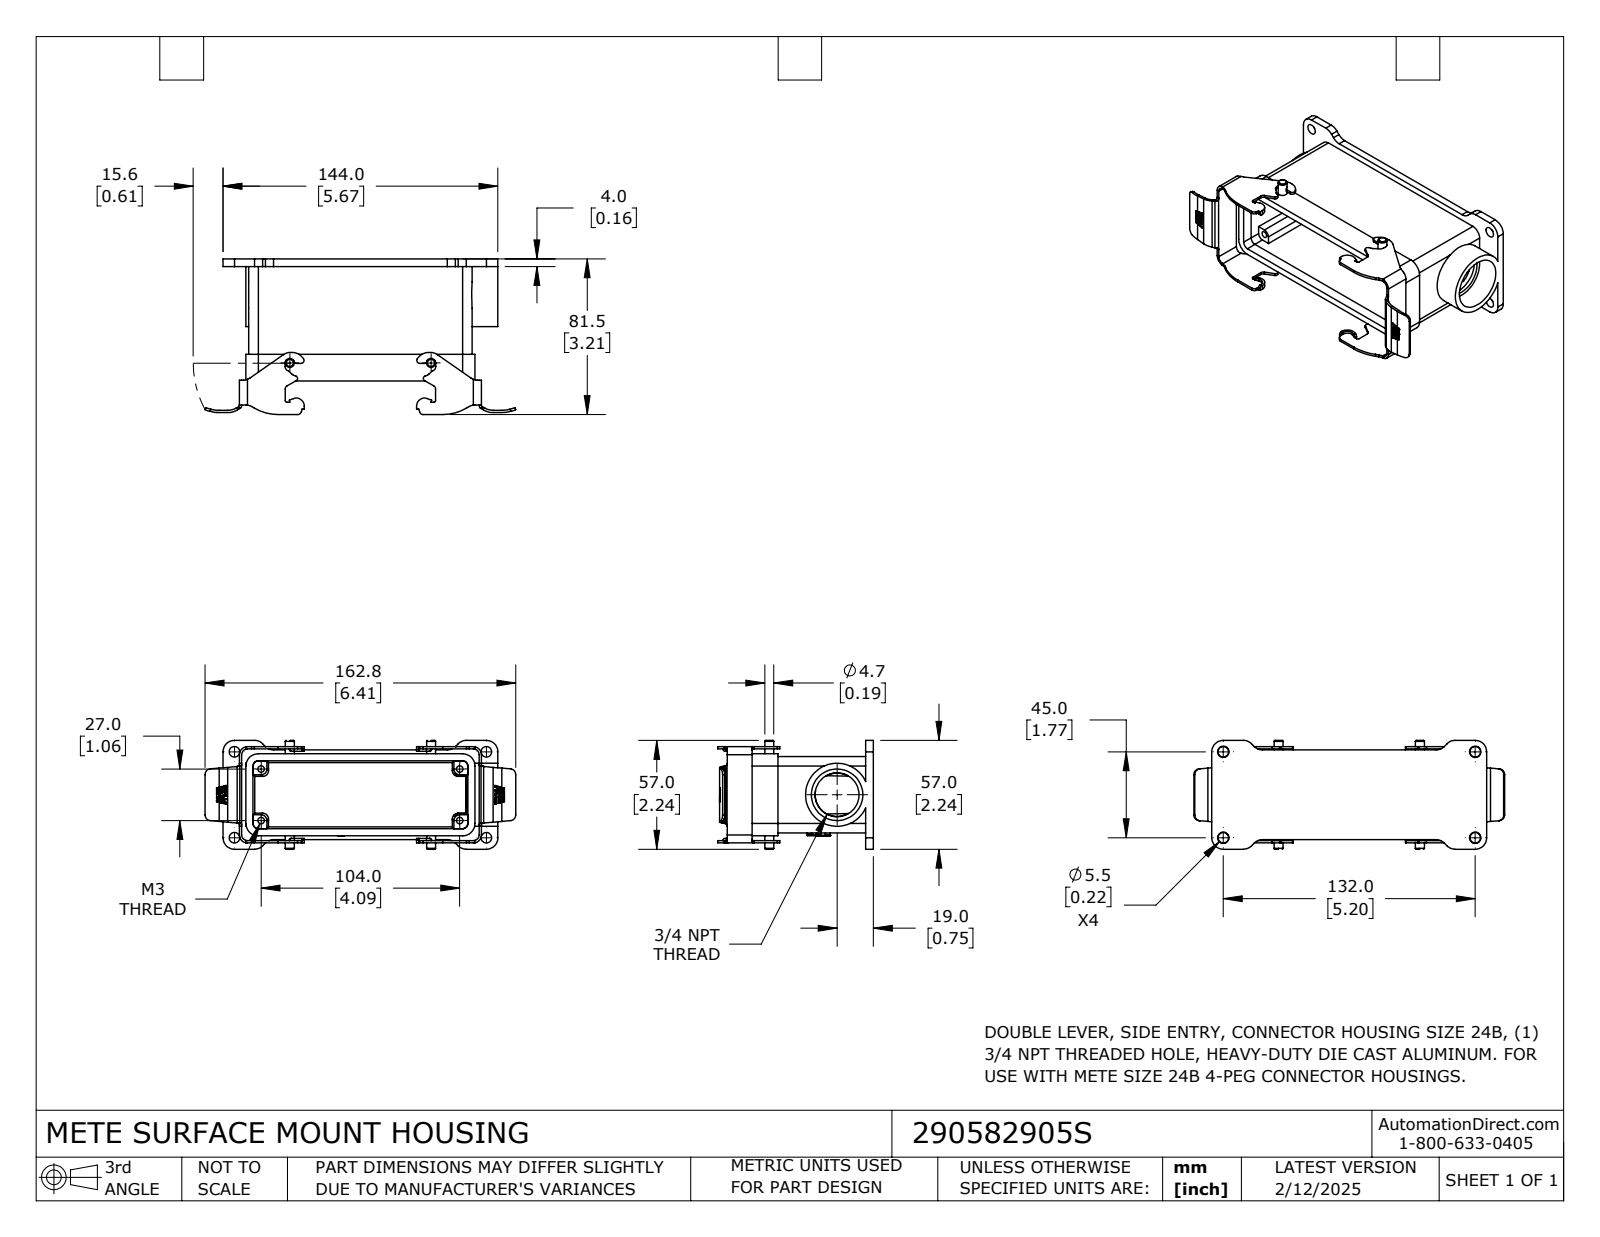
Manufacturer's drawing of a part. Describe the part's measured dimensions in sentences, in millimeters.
The part is named "290582905S". Its 3-D file was written by "SolidWorks 2024 (CONFIG_CONTROL_DESIGN)". It is 1 solid with 496 faces: 222 planar, 244 cylindrical and 30 other. Overall it measures 162.8 by 81.5 by 57 millimeters. Its volume is 101 500 cubic millimeters and its surface area 65 810 square millimeters. Round holes: 4 of diameter 3.4, 1 of diameter 23, 1 of diameter 27. Round bosses or shafts: 2 of diameter 4.7, 1 of diameter 33. Partial cylindrical surfaces (rounded edges, fillets, slot ends): 57 of radius 0.2, 16 of radius 6, 14 of radius 3, 10 of radius 1, 6 of radius 1.5, 6 of radius 2, 6 of radius 2.5, 6 of radius 4.2. The main face-to-face distances are 4, 3.7, 40, 1.5, 1.2, 41.5, 2.2, 43, 5.2, 45.2. The hole center spacings are 27, 104, 107.4.
